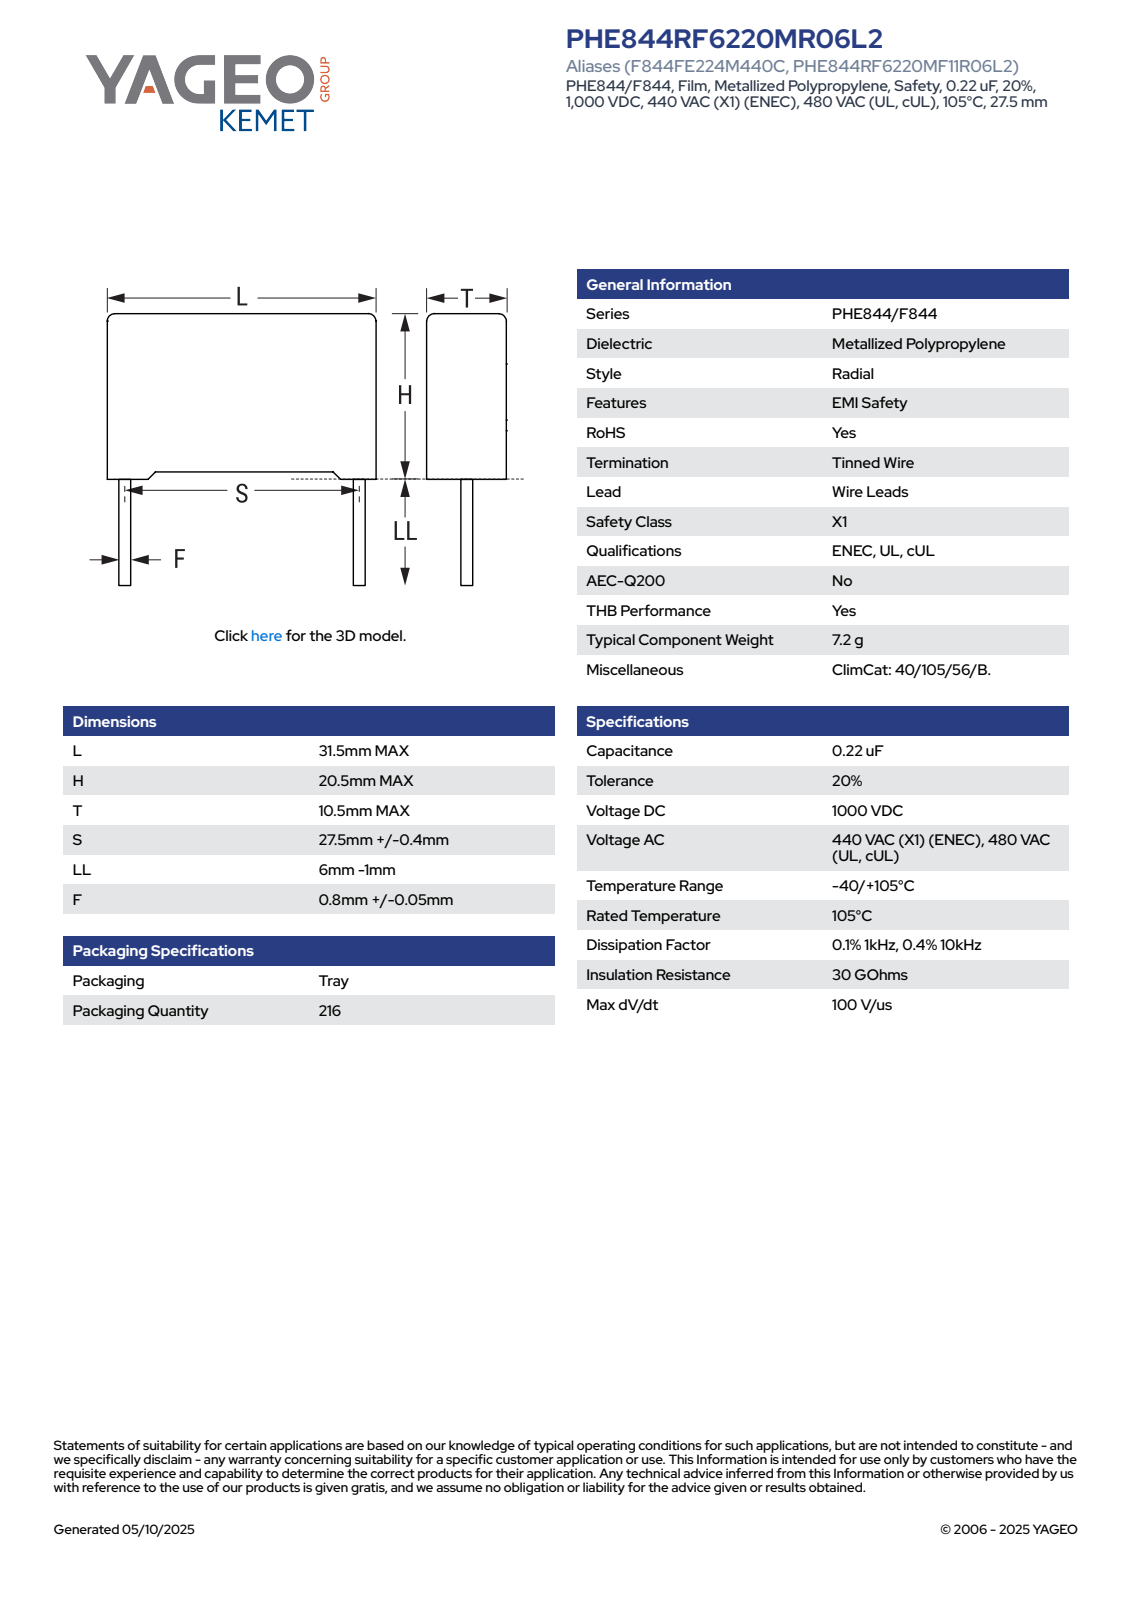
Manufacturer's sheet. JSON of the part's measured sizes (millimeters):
{"part_name": "CFR_RB2_31.5X20.5X10.5_L31.5H20.5T10.5S27.5LL5F0.85", "step_written_by": "SolidWorks 2021 (AUTOMOTIVE_DESIGN)", "units": "millimeters", "bodies": {"solids": 4, "faces": 85, "planar": 77, "cylindrical": 8, "other": 0}, "overall_size": [31.5, 25.5, 10.51], "volume_mm3": 6562, "surface_area_mm2": 2461, "round_bosses_or_shafts": [[0.85, 2]], "partial_cylinders_radius": [[0.5, 4]], "face_to_face_distances": [10.5, 19.75, 31.5, 19.79, 0.71, 0.75, 20.5, 1.05, 10.51, 30.45]}
